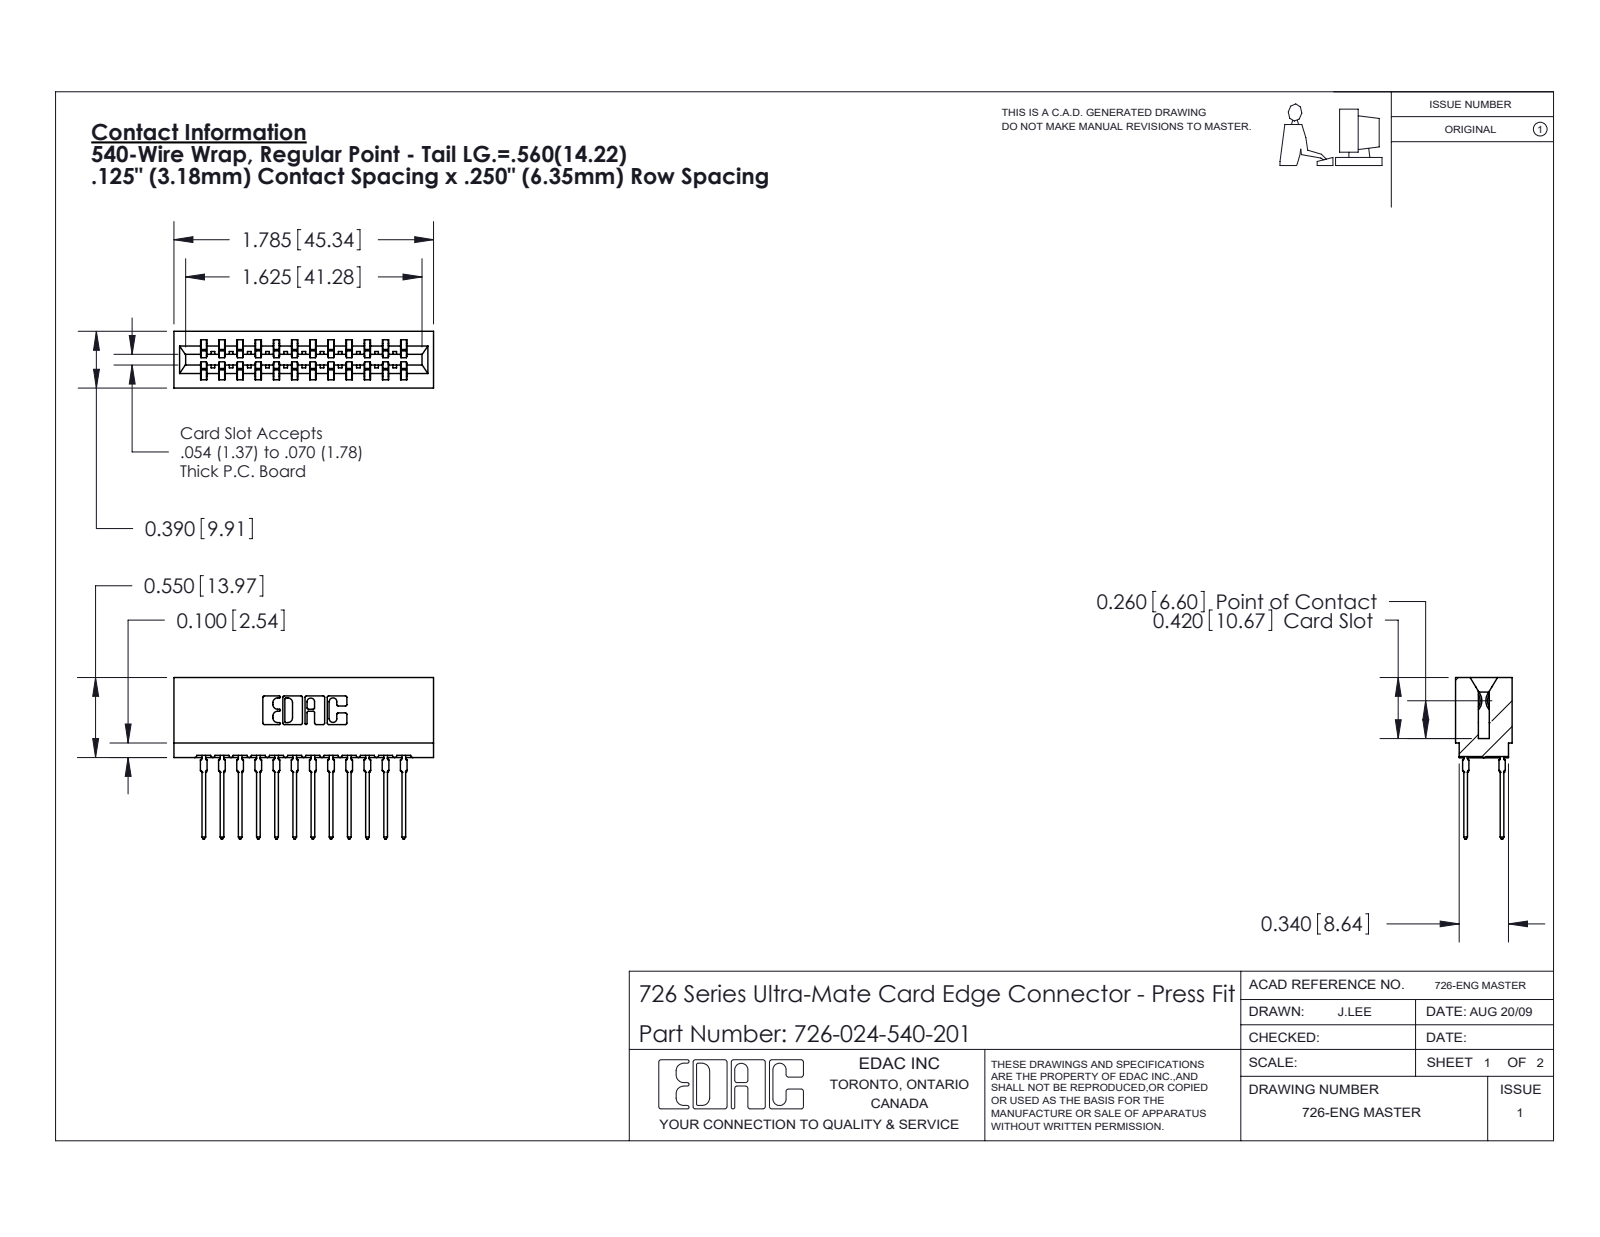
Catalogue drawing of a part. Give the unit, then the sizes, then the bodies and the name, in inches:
Units: inches
Overall size (bounding box): 1.785 × 1.109 × 0.39
Partial cylindrical surfaces — rounded edges, fillets, slot ends (radius × count): R0.021 ×48, R0.01 ×22, R0.015 ×13, R0.005 ×8, R0.011 ×8, R0.007 ×6, R0.031 ×6, R0.026 ×3
Main face-to-face distances: 0.25, 0.057, 0.333, 0.5, 0.025, 0.307, 0.083, 0.39, 0.125, 0.75
Volume: 0.269 in³ · Surface area: 11.07 in²
Bodies: 25 solids, 2245 faces (1159 planar, 462 cylindrical, 624 other)
Part name (STEP PRODUCT): 726-024-540-201; 726 Part_.515 Slot Depth - 01; 746-292-001_540
STEP written by: SolidWorks 2020 (CONFIG_CONTROL_DESIGN)
